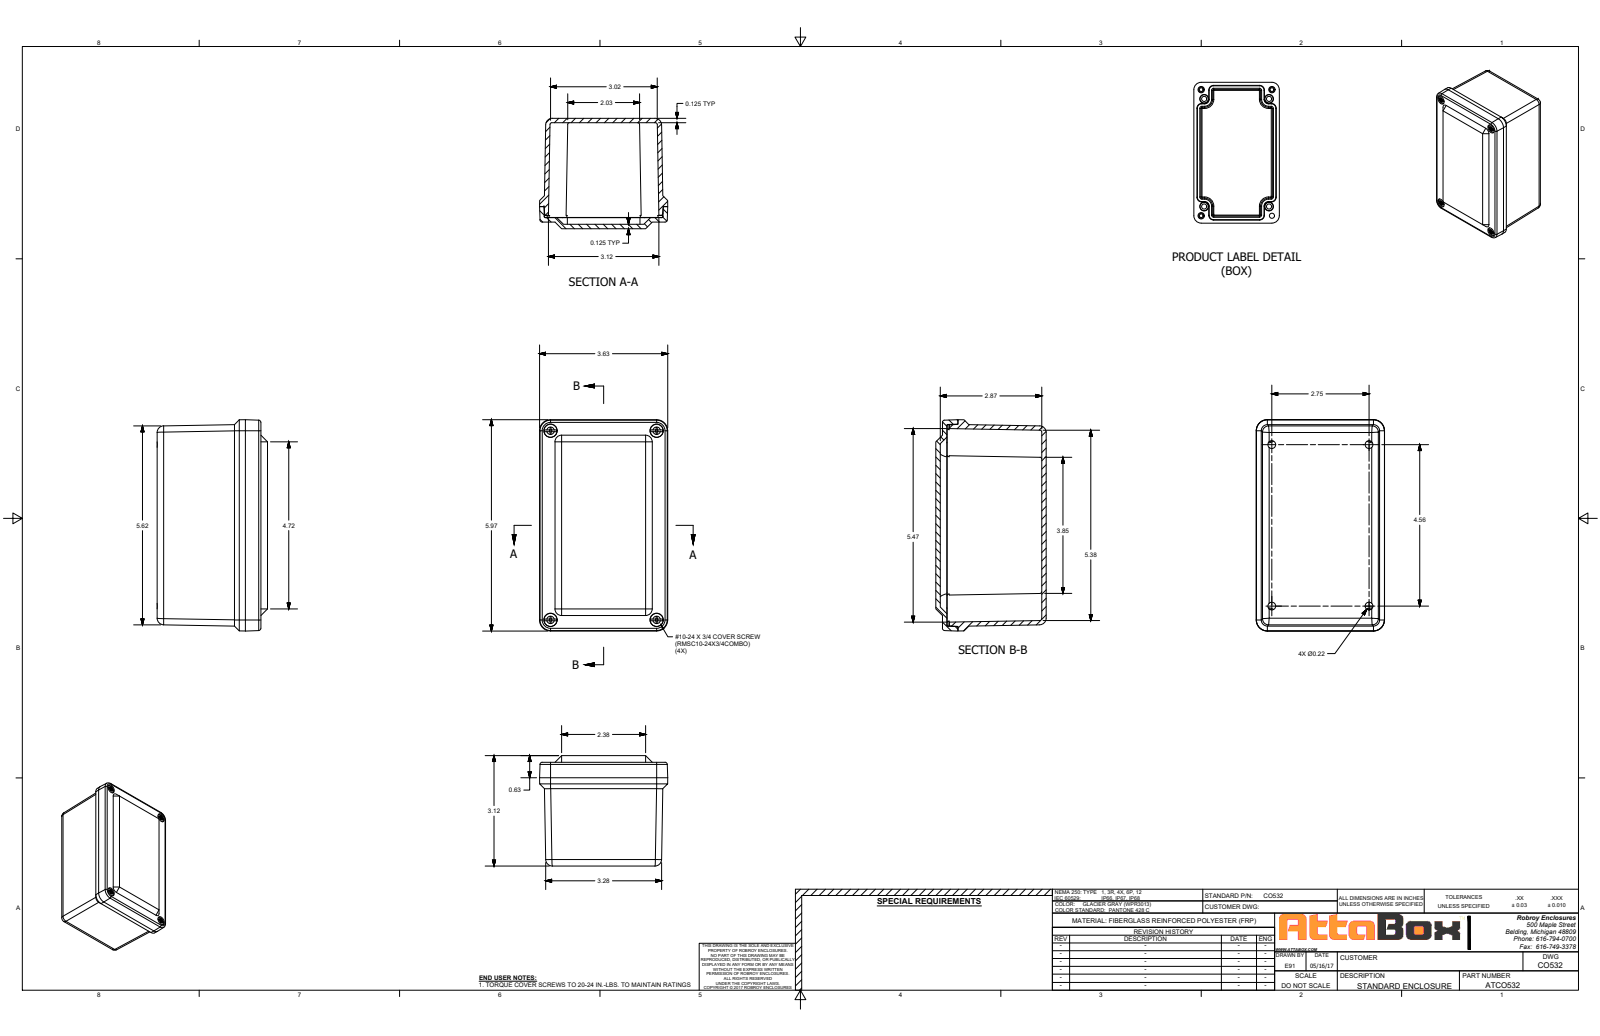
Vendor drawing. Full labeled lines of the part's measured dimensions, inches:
Part name (STEP PRODUCT): CO532
STEP written by: SolidWorks 2018 (AUTOMOTIVE_DESIGN)
Units: inches
Bodies: 11 solids, 375 faces (167 planar, 112 cylindrical, 96 other)
Overall size (bounding box): 5.971 × 3.625 × 3.12
Volume: 14.69 in³ · Surface area: 211.2 in²
Round holes (diameter × count): ⌀0.219 ×8, ⌀0.159 ×4, ⌀0.19 ×4, ⌀0.375 ×4
Round bosses / shafts (diameter × count): ⌀0.371 ×4, ⌀0.27 ×4, ⌀0.177 ×4
Partial cylindrical surfaces — rounded edges, fillets, slot ends (radius × count): R0.031 ×20, R0.012 ×16, R0.048 ×8, R0.176 ×4, R0.22 ×4, R0.313 ×4, R0.325 ×4, R0.188 ×3
Main face-to-face distances: 0.122, 0.125, 0.125, 3.12, 2.995, 0.187, 2.995, 2.87, 0.5, 0.313
Hole centre spacings: 0.411, 2.901, 4.955, 5.727, 2.75, 3, 4.562, 5.327
